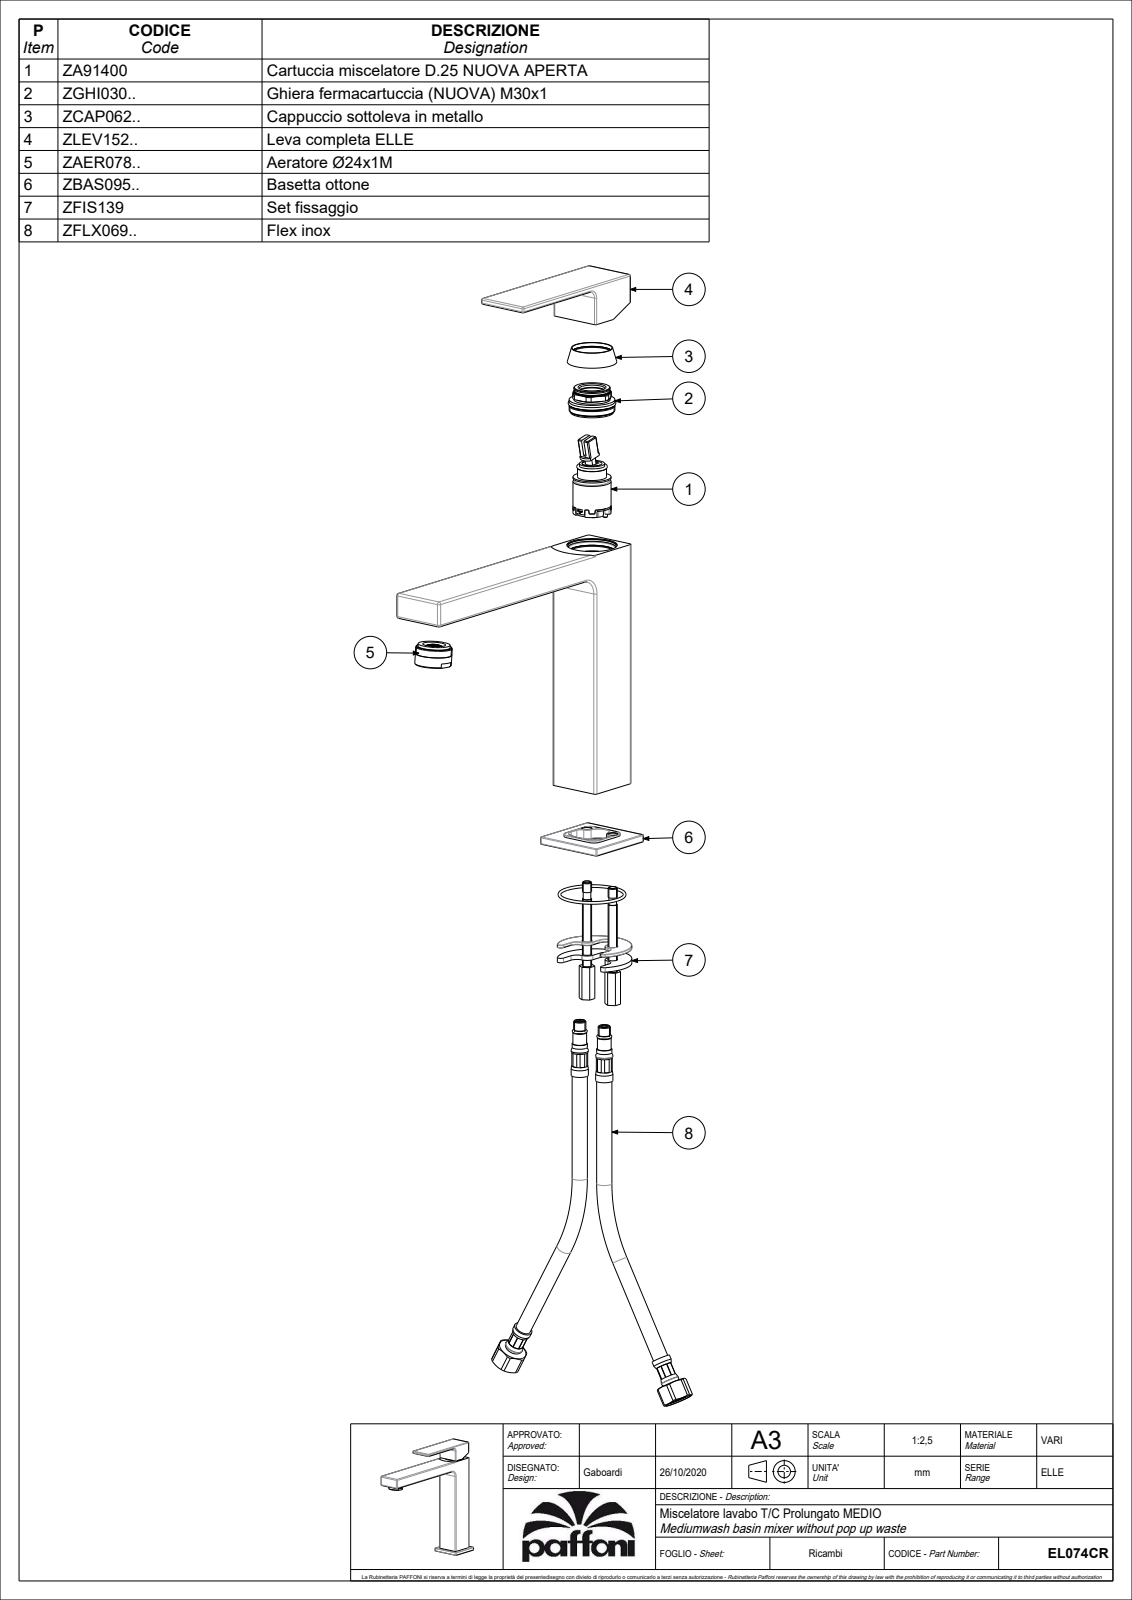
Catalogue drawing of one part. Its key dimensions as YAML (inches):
part_name: "EL074CR"
step_written_by: "CREO PARAMETRIC BY PTC INC, 2020044 (CONFIG_CONTROL_DESIGN)"
units: inches
bodies: {solids: 2, faces: 179, planar: 57, cylindrical: 72, other: 50}
overall_size: [7.953, 7.728, 1.89]
volume: 22.24
surface_area: 98.74
round_holes:
  - {diameter: 0.118, count: 1}
  - {diameter: 0.177, count: 1}
  - {diameter: 0.217, count: 1}
  - {diameter: 0.965, count: 1}
  - {diameter: 0.976, count: 1}
  - {diameter: 1.031, count: 1}
  - {diameter: 1.102, count: 1}
round_bosses_or_shafts:
  - {diameter: 0.945, count: 1}
partial_cylinders:
  - {radius: 0.059, count: 20}
  - {radius: 0.039, count: 13}
  - {radius: 0.02, count: 12}
  - {radius: 0.197, count: 1}
  - {radius: 0.394, count: 1}
  - {radius: 1.083, count: 1}
face_to_face_distances: [1.457, 0.669, 1.783, 1.113, 0.02, 7.728, 0.956, 1.625, 0.157, 5.945]
